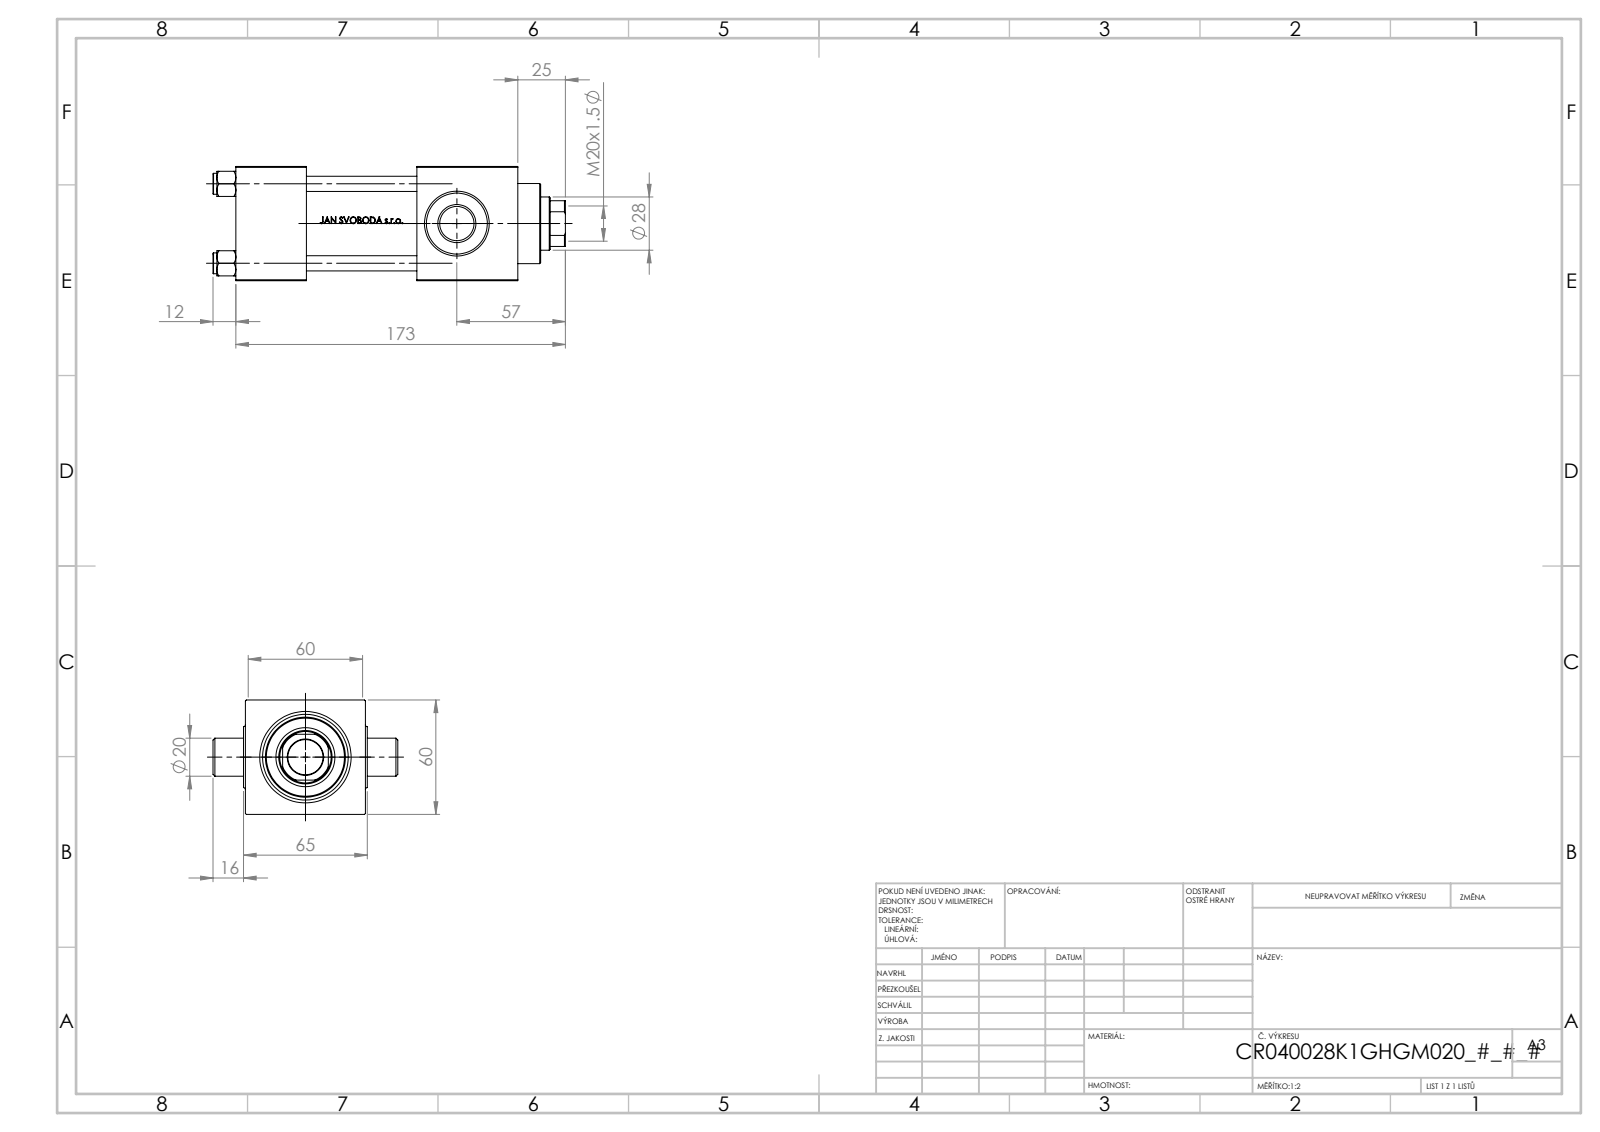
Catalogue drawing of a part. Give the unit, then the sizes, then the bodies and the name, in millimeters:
Units: millimetres
Overall size (bounding box): 185 × 97 × 60
Round holes (diameter × count): ⌀8 ×4, ⌀2.5 ×2, ⌀7 ×1, ⌀18.5 ×1, ⌀28 ×1, ⌀31 ×1, ⌀40 ×1, ⌀45 ×1
Round bosses / shafts (diameter × count): ⌀11 ×4, ⌀46 ×1, ⌀42 ×1, ⌀20 ×1
Partial cylindrical surfaces — rounded edges, fillets, slot ends (radius × count): R13.5 ×1
Main face-to-face distances: 60, 1.5, 61.5, 37, 63, 95, 58, 148, 111, 53
Hole centre spacings: 20.85, 29.49, 41.7, 46.53, 20.75, 58.97, 41.5
Volume: 453 951 mm³ · Surface area: 109 743 mm²
Bodies: 11 solids, 1065 faces (429 planar, 114 cylindrical, 522 other)
Part name (STEP PRODUCT): V215CR_VCP_K; V215CR_K_TYCINKA; V215_VC_A; V215CR_K_Body (+1 more)
STEP written by: SolidWorks 2019 (CONFIG_CONTROL_DESIGN)
